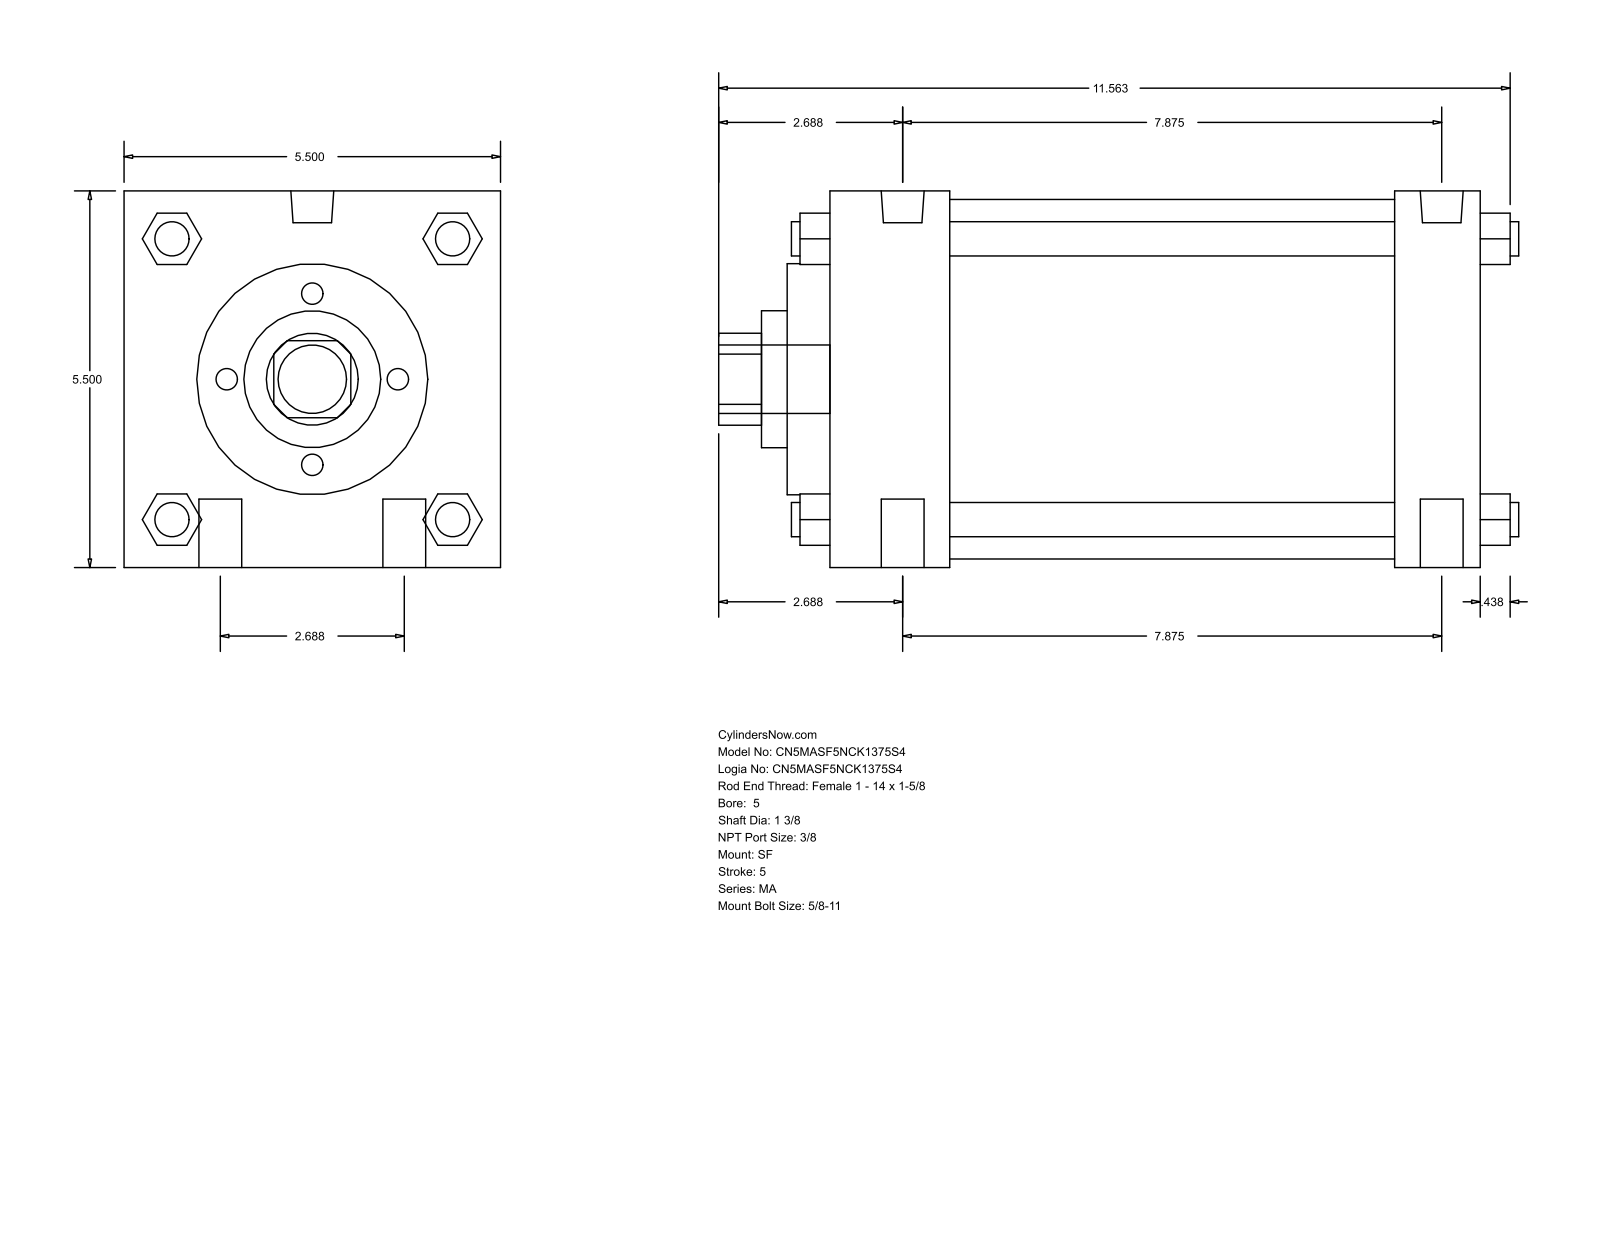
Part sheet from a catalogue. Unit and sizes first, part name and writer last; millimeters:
Units: millimetres
Overall size (bounding box): 296.86 × 139.7 × 139.7
Round holes (diameter × count): ⌀34.92 ×1, ⌀50.8 ×1, ⌀85.72 ×1, ⌀133.35 ×1
Round bosses / shafts (diameter × count): ⌀15.88 ×4, ⌀12.7 ×4, ⌀15.93 ×2, ⌀11.11 ×2, ⌀25.4 ×1
Partial cylindrical surfaces — rounded edges, fillets, slot ends (radius × count): R17.06 ×1
Main face-to-face distances: 139.7, 241.3, 44.45, 209.55, 165.1, 196.85, 31.75, 15.87, 60.32, 225.42
Bodies: 0 solids, 126 faces (95 planar, 31 cylindrical, 0 other)
Part name (STEP PRODUCT): MA_SF__0500_1.375
STEP written by: GSSL Pune (CONFIG_CONTROL_DESIGN)
